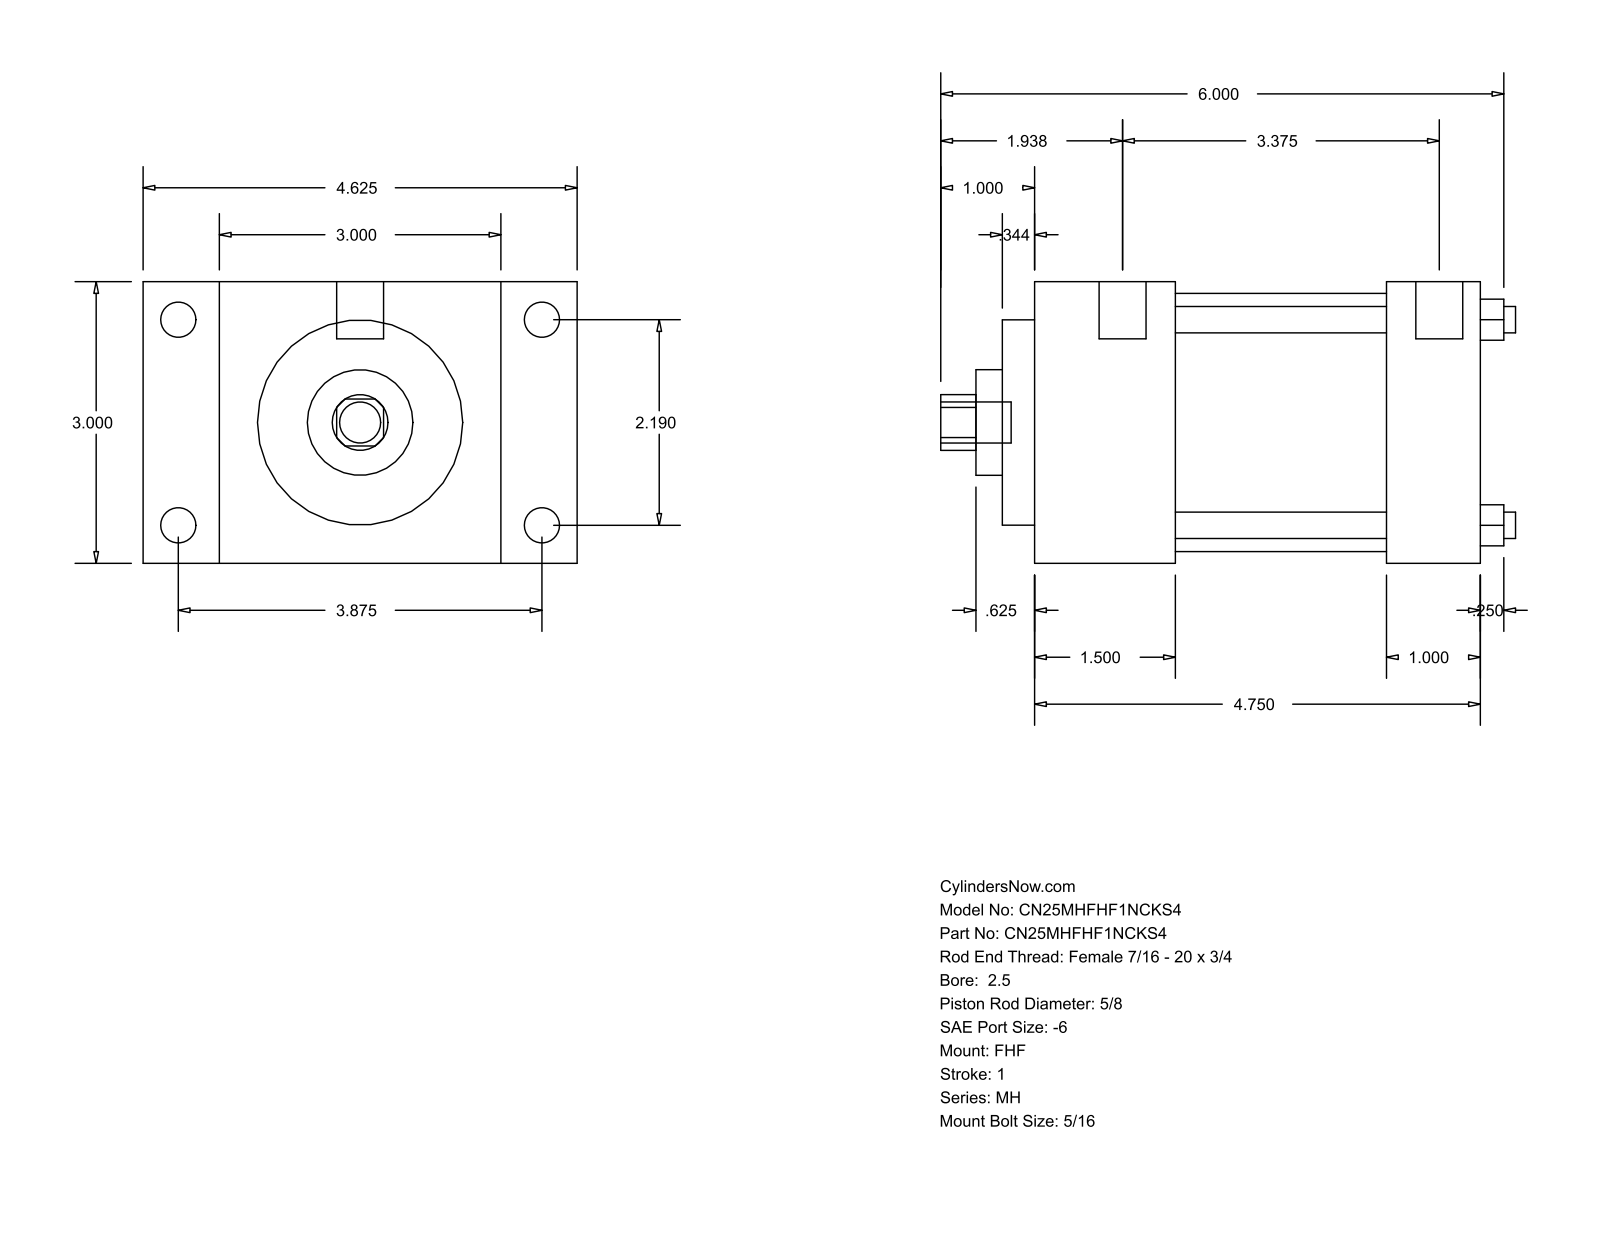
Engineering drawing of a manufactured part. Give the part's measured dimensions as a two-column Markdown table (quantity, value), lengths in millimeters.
| quantity | value |
| --- | --- |
| part name | MH_FHF__0250_0.625 |
| STEP written by | GSSL Pune (CONFIG_CONTROL_DESIGN) |
| units | millimeters |
| bodies | 0 solids, 90 faces (61 planar, 29 cylindrical, 0 other) |
| overall size | 155.57 × 117.47 × 76.2 |
| round holes (diameter × count) | 7.14 × 4, 15.88 × 1, 28.57 × 1, 55.55 × 1, 69.85 × 1 |
| round bosses / shafts (diameter × count) | 9.53 × 4, 5.56 × 4, 12.7 × 2, 11.11 × 1 |
| partial cylindrical surfaces (radius × count) | 7.54 × 1 |
| main face-to-face distances | 76.2, 120.65, 38.1, 82.55, 20.64, 96.84, 117.48, 25.4, 57.15, 95.25 |
| hole center spacings | 39.33, 55.62, 78.66 |
